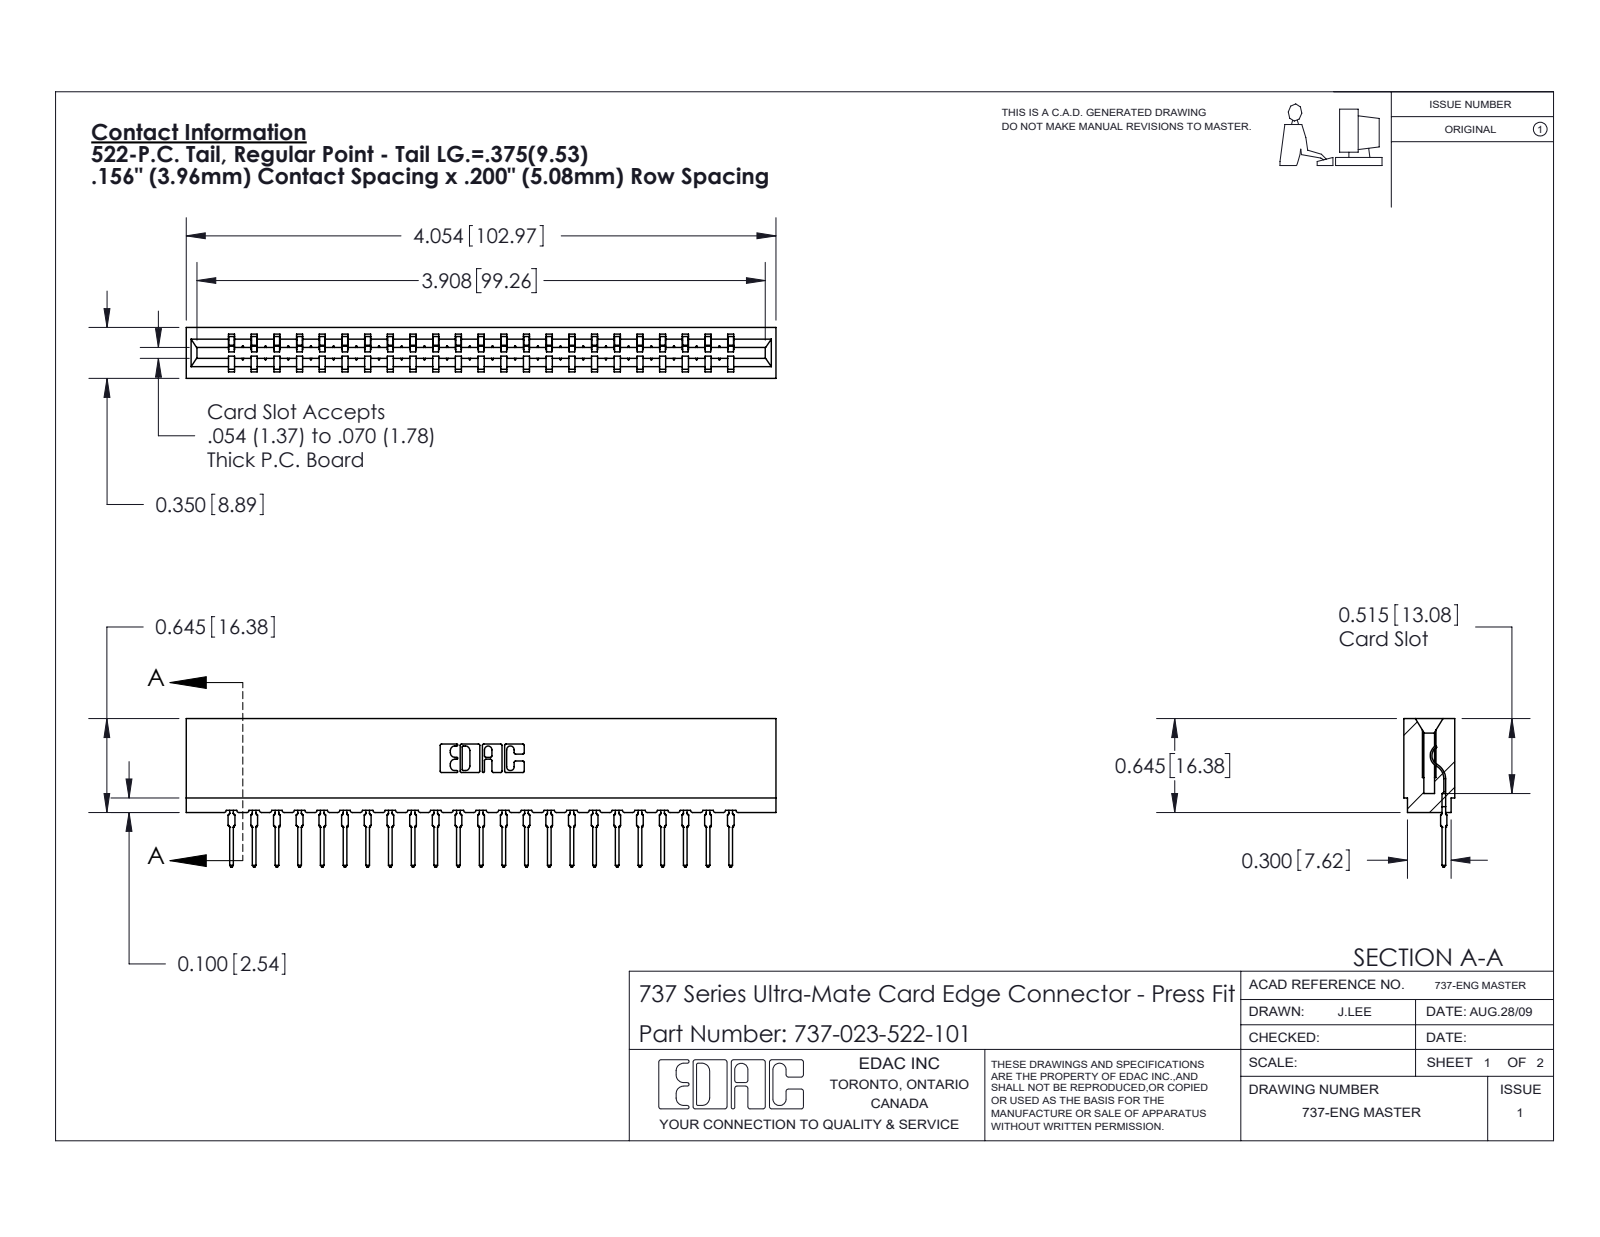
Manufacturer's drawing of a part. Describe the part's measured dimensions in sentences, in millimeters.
The part is named "737-023-522-101; 745-292-001_522; 737 Part_Insulator Option - 01". Its 3-D file was written by "SolidWorks 2020 (CONFIG_CONTROL_DESIGN)". It is 24 solids with 2693 faces: 1618 planar, 477 cylindrical and 598 other. Overall it measures 103 by 25.9 by 8.9 millimeters. Its volume is 10 100 cubic millimeters and its surface area 13 280 square millimeters. Partial cylindrical surfaces (rounded edges, fillets, slot ends): 46 of radius 0.4, 46 of radius 0.5, 22 of radius 0.3, 6 of radius 0.2, 6 of radius 0.8, 4 of radius 0.1, 4 of radius 0.3, 3 of radius 0.7. The main face-to-face distances are 3.5, 5.4, 8.9, 4, 15.8, 1.9, 1.1, 7.7, 2.4, 4.2.
